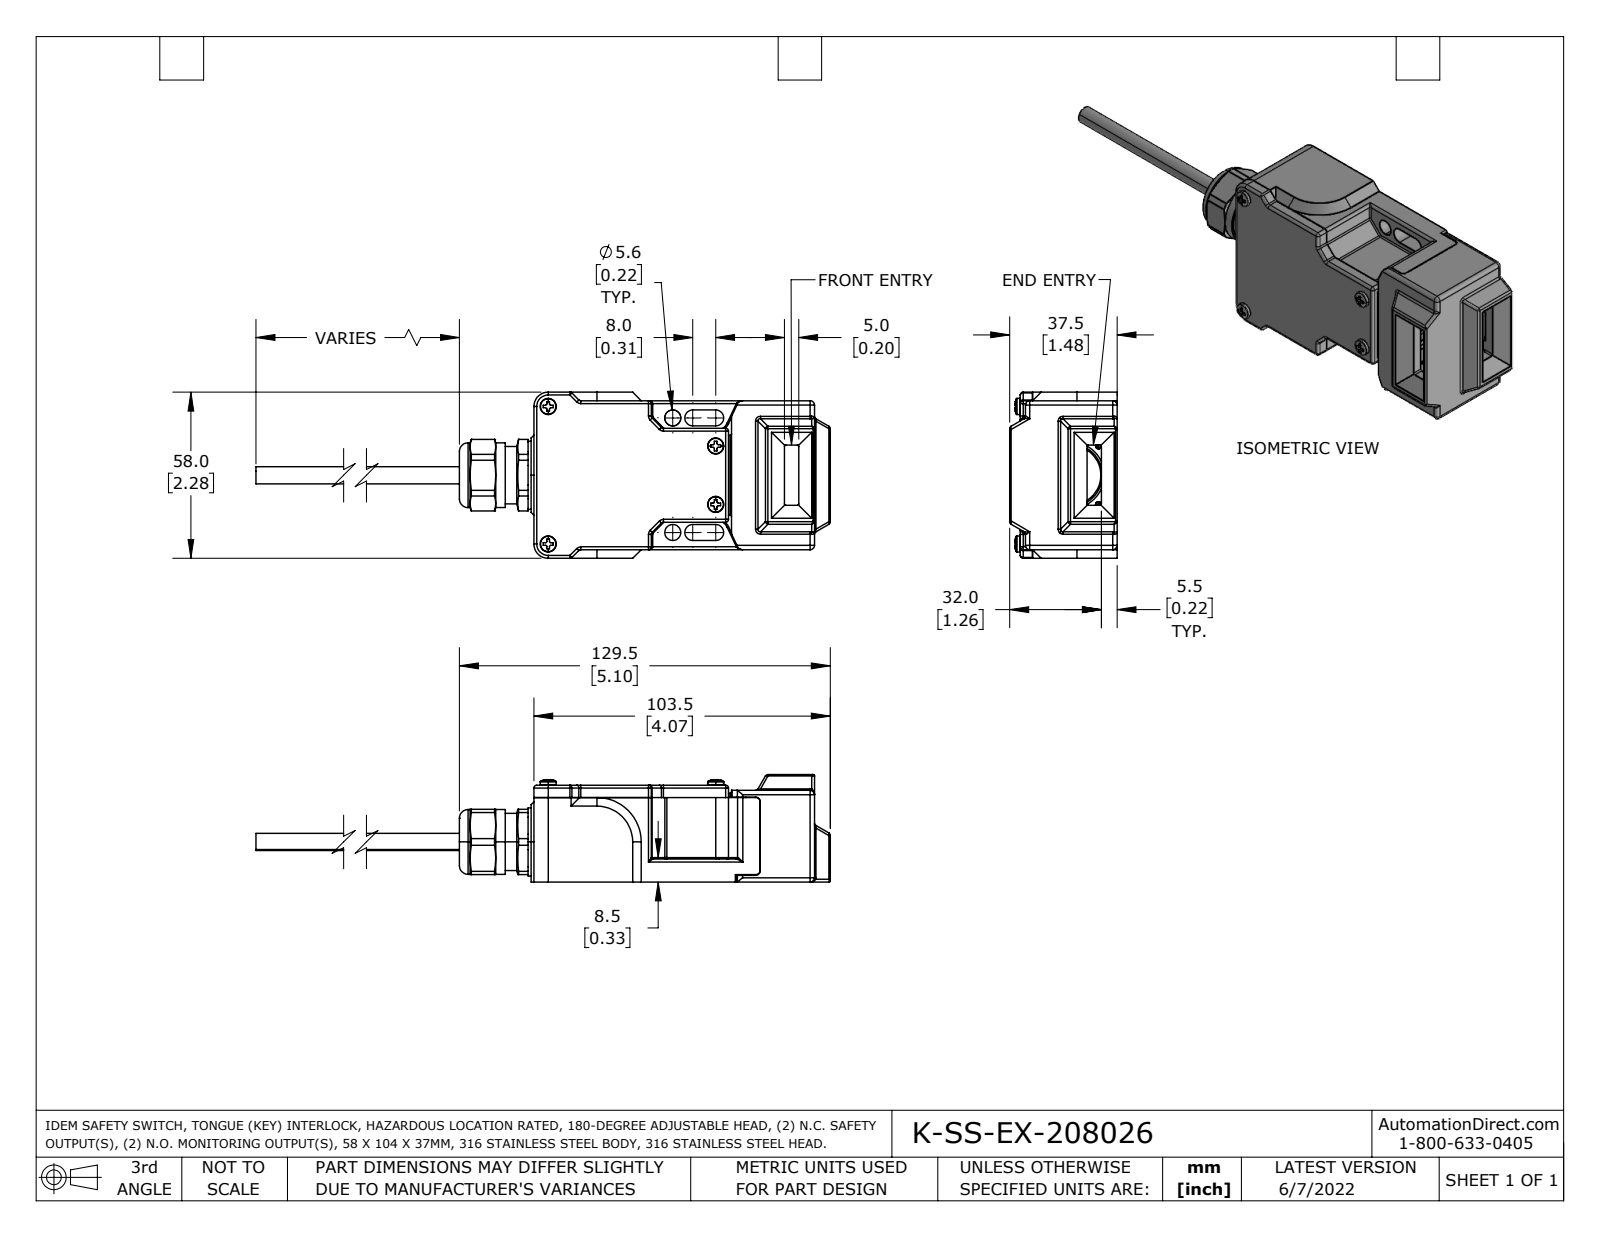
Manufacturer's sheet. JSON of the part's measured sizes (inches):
{"part_name": "K-SS-EX-208026", "step_written_by": "SolidWorks 2021 (AUTOMOTIVE_DESIGN)", "units": "inches", "bodies": {"solids": 14, "faces": 1439, "planar": 540, "cylindrical": 588, "other": 311}, "overall_size": [7.776, 2.283, 1.476], "volume_in3": 4.721, "surface_area_in2": 92.01, "round_holes": [[0.118, 4], [0.146, 4], [0.079, 2], [0.102, 2], [0.126, 2], [0.177, 2], [0.197, 2], [0.22, 2], [0.15, 1], [0.248, 1], [0.276, 1], [0.504, 1]], "round_bosses_or_shafts": [[0.22, 4], [0.256, 2], [0.177, 2], [0.134, 2], [0.106, 2], [0.071, 2], [0.937, 1], [0.89, 1]], "partial_cylinders_radius": [[0.02, 203], [0.039, 83], [0.059, 14], [0.012, 12], [0.079, 8], [0.11, 4], [0.098, 2], [0.118, 2]], "face_to_face_distances": [0.118, 0.098, 0.039, 1.331, 2.047, 1.291, 1.232, 1.193, 0.063, 0.079], "hole_center_spacings": [0.404, 0.498, 0.549, 0.706, 0.803, 0.827, 0.906, 1.008]}
